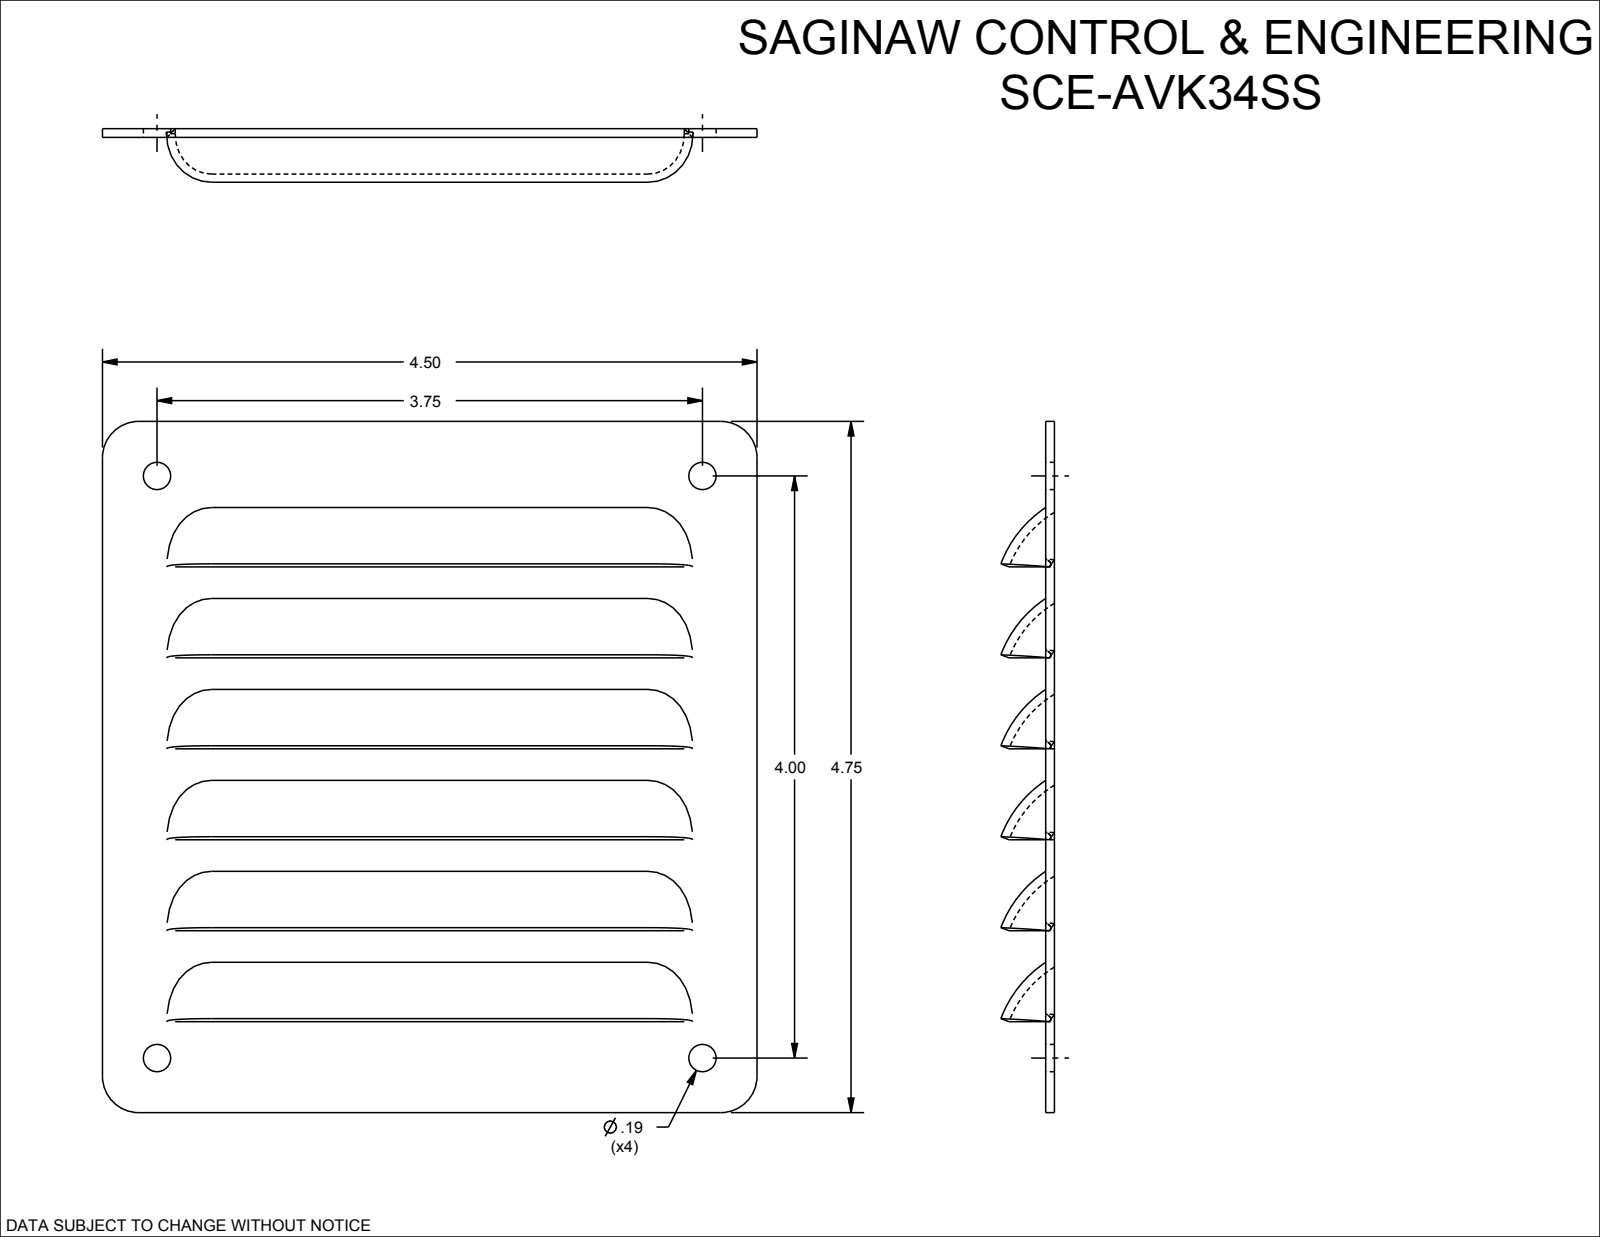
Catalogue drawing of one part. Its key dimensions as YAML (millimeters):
part_name: "SCE-AVK34SS"
step_written_by: "SolidWorks 2021 (AUTOMOTIVE_DESIGN)"
units: millimeters
bodies: {solids: 1, faces: 108, planar: 24, cylindrical: 36, other: 48}
overall_size: [120.7, 114.3, 11.9]
volume: 23890
surface_area: 33630
round_holes:
  - {diameter: 4.7, count: 4}
partial_cylinders:
  - {radius: 18.8, count: 6}
  - {radius: 20.3, count: 6}
  - {radius: 6.4, count: 4}
face_to_face_distances: [1.5, 31.8, 15.9, 15.9, 7.4, 24.4, 63.5, 29.7, 47.6, 47.6]
hole_center_spacings: [95.3, 101.6, 139.3]
